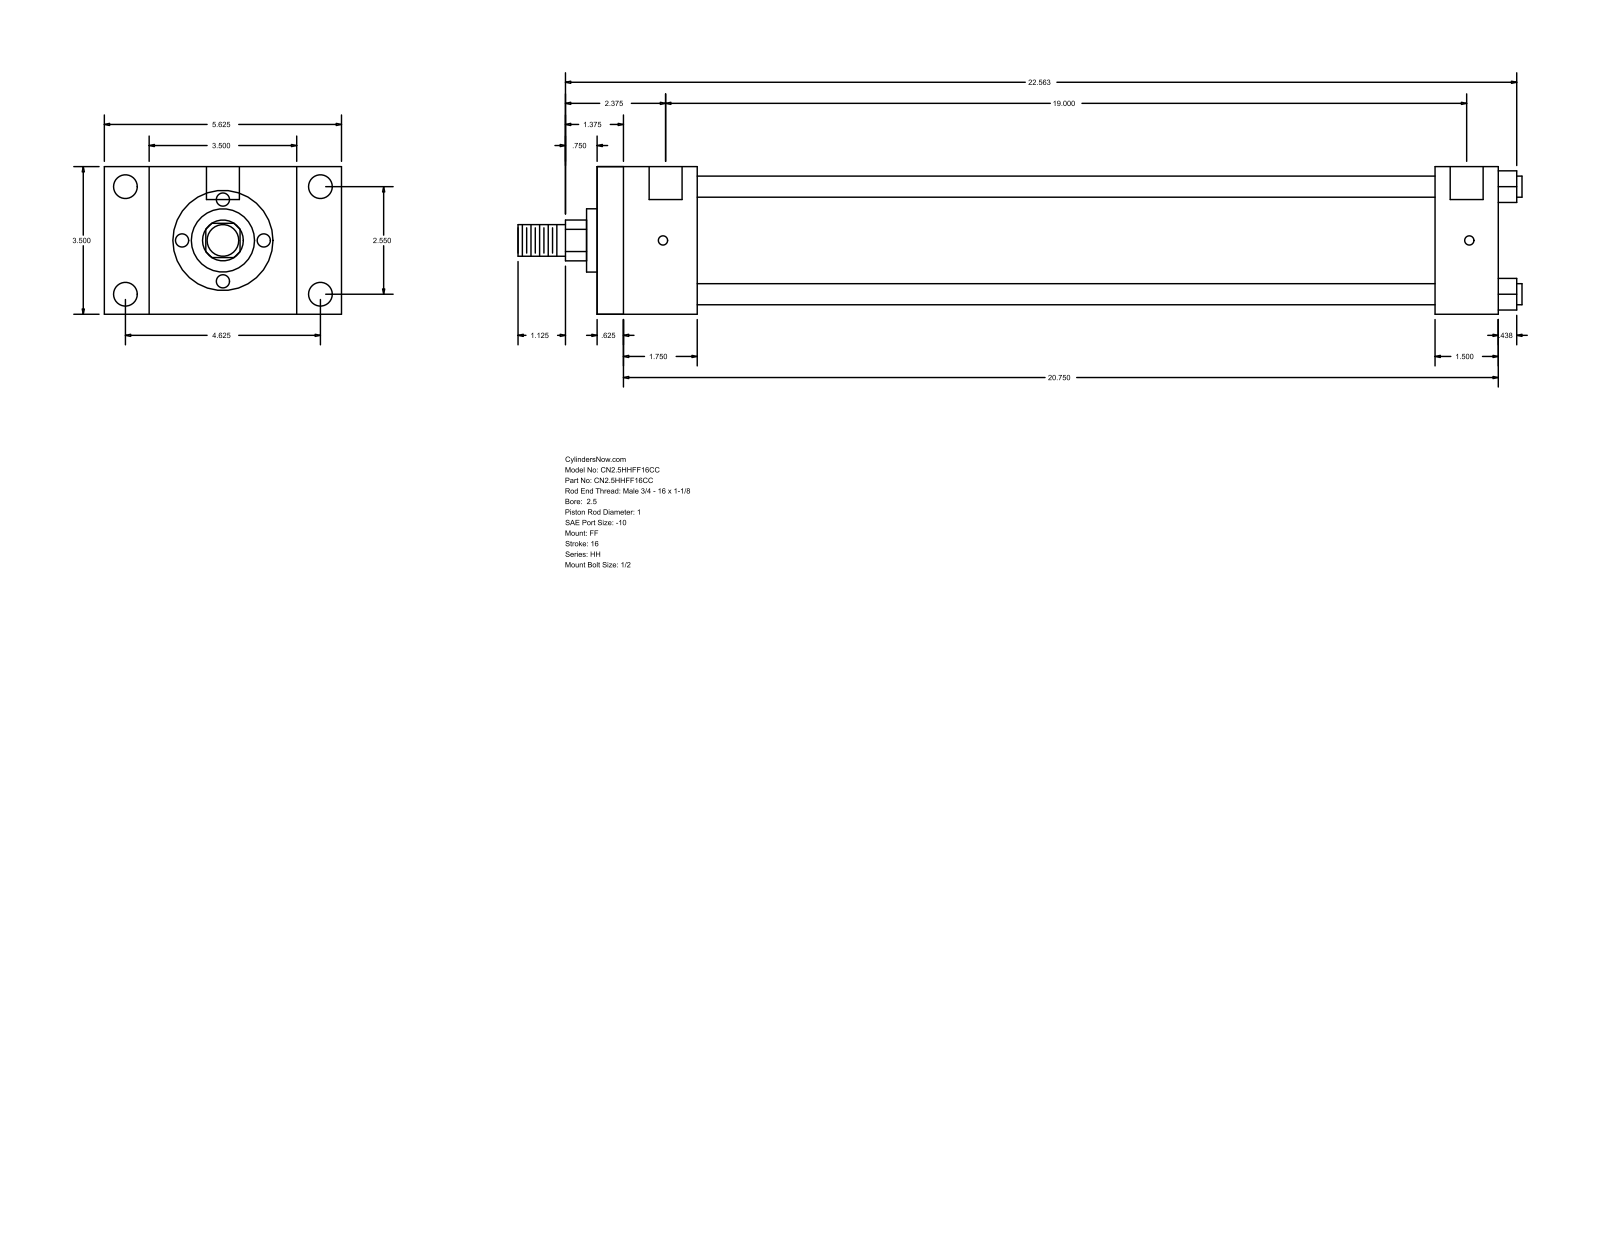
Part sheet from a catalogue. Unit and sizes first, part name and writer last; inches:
Units: inches
Overall size (bounding box): 23.813 × 5.625 × 3.5
Round holes (diameter × count): ⌀0.219 ×4, ⌀0.563 ×4, ⌀0.781 ×2
Round bosses / shafts (diameter × count): ⌀0.5 ×4, ⌀2.875 ×1, ⌀1.5 ×1, ⌀1 ×1, ⌀0.75 ×1
Partial cylindrical surfaces — rounded edges, fillets, slot ends (radius × count): R0.484 ×1
Main face-to-face distances: 3.5, 21.375, 0.625, 20.75, 1.5, 2.375, 1.75, 19, 19.875, 19.25
Hole centre spacings: 0.063, 2.55, 4.625, 5.281, 19.062, 19.125, 19
Bodies: 0 solids, 92 faces (64 planar, 28 cylindrical, 0 other)
Part name (STEP PRODUCT): HH_FF__0250_1
STEP written by: GSSL Pune (CONFIG_CONTROL_DESIGN)
